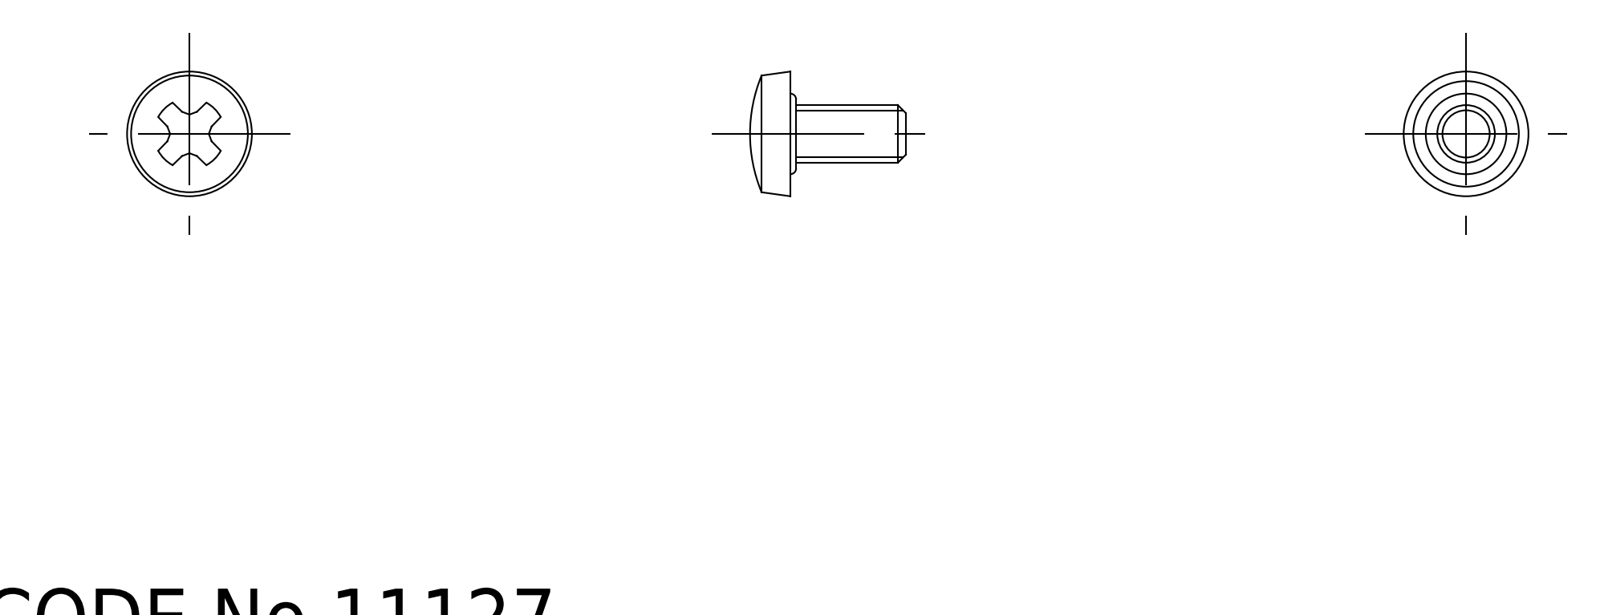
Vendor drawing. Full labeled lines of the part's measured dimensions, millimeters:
Part name (STEP PRODUCT): screw; TL_417_M3_6
STEP written by: SolidWorks 2015 (AUTOMOTIVE_DESIGN)
Units: millimetres
Bodies: 2 solids, 38 faces (20 planar, 8 cylindrical, 10 other)
Overall size (bounding box): 8.04 × 6.5 × 6.5
Volume: 90 mm³ · Surface area: 185 mm²
Round holes (diameter × count): ⌀5.5 ×1
Round bosses / shafts (diameter × count): ⌀3 ×1
Partial cylindrical surfaces — rounded edges, fillets, slot ends (radius × count): R1.85 ×1
Main face-to-face distances: 1, 1.3, 7.3, 6.3, 6, 1.12, 1.88
